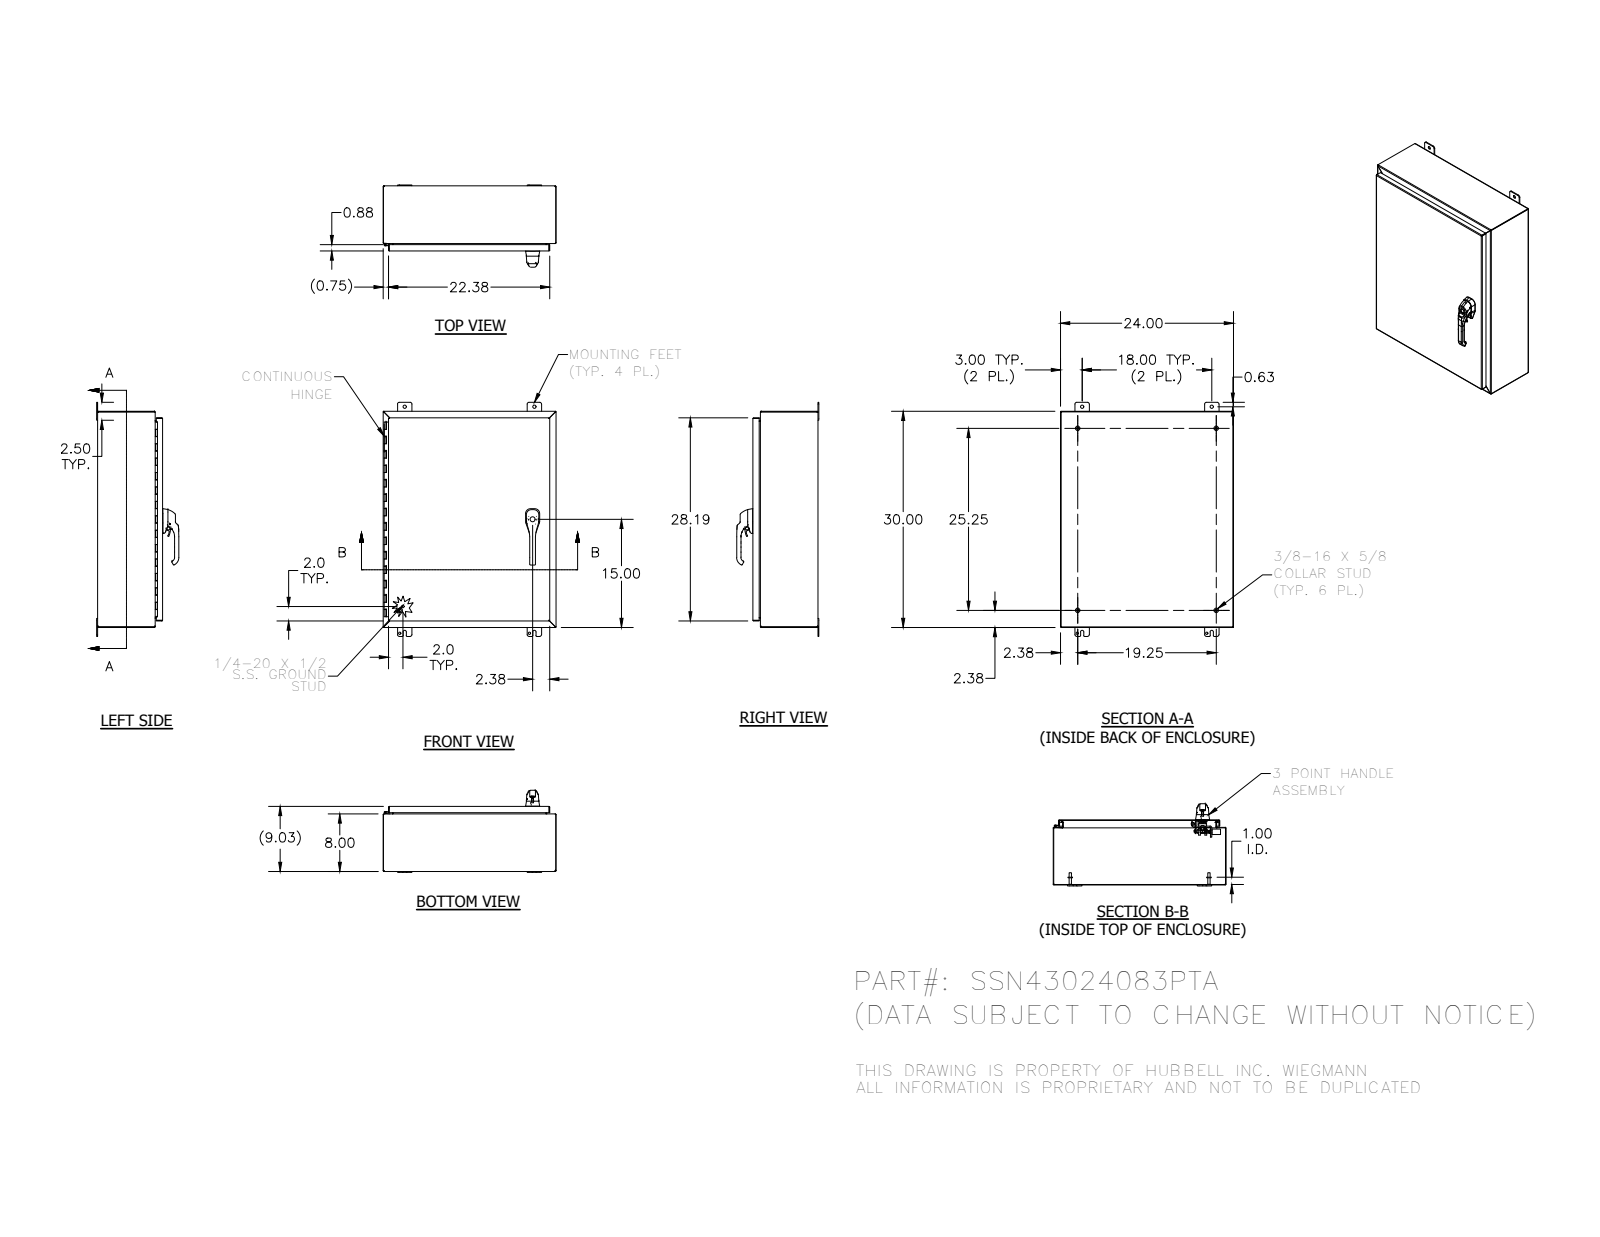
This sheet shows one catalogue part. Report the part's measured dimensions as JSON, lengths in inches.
{"part_name": "SPACER; DIN3771_16X2_5; 37039; 1091-BR11_AF0 (+8 more)", "step_written_by": "SolidWorks 2014 (AUTOMOTIVE_DESIGN)", "units": "inches", "bodies": {"solids": 56, "faces": 3136, "planar": 1047, "cylindrical": 1304, "other": 785}, "overall_size": [32.5, 24, 11.408], "volume_in3": 217.2, "surface_area_in2": 5615, "round_holes": [[0.262, 8], [0.187, 4], [0.313, 4], [0.438, 4], [0.213, 3], [0.281, 3], [0.241, 2], [0.25, 2], [0.252, 2], [0.315, 2], [0.4, 2], [0.402, 2]], "round_bosses_or_shafts": [[0.625, 4], [0.33, 4], [0.236, 3], [1, 2], [0.563, 2], [0.533, 2], [0.531, 2], [0.5, 2]], "partial_cylinders_radius": [[0.02, 172], [0.012, 113], [0.125, 26], [0.031, 24], [0.019, 21], [0.105, 20], [0.25, 20], [0.025, 16]], "face_to_face_distances": [0.074, 8.959, 8.885, 9.033, 23.926, 29.926, 7.926, 1.033, 23.852, 24], "hole_center_spacings": [0.38, 0.492, 0.76, 1.593, 18, 30, 34.986, 0.886]}
